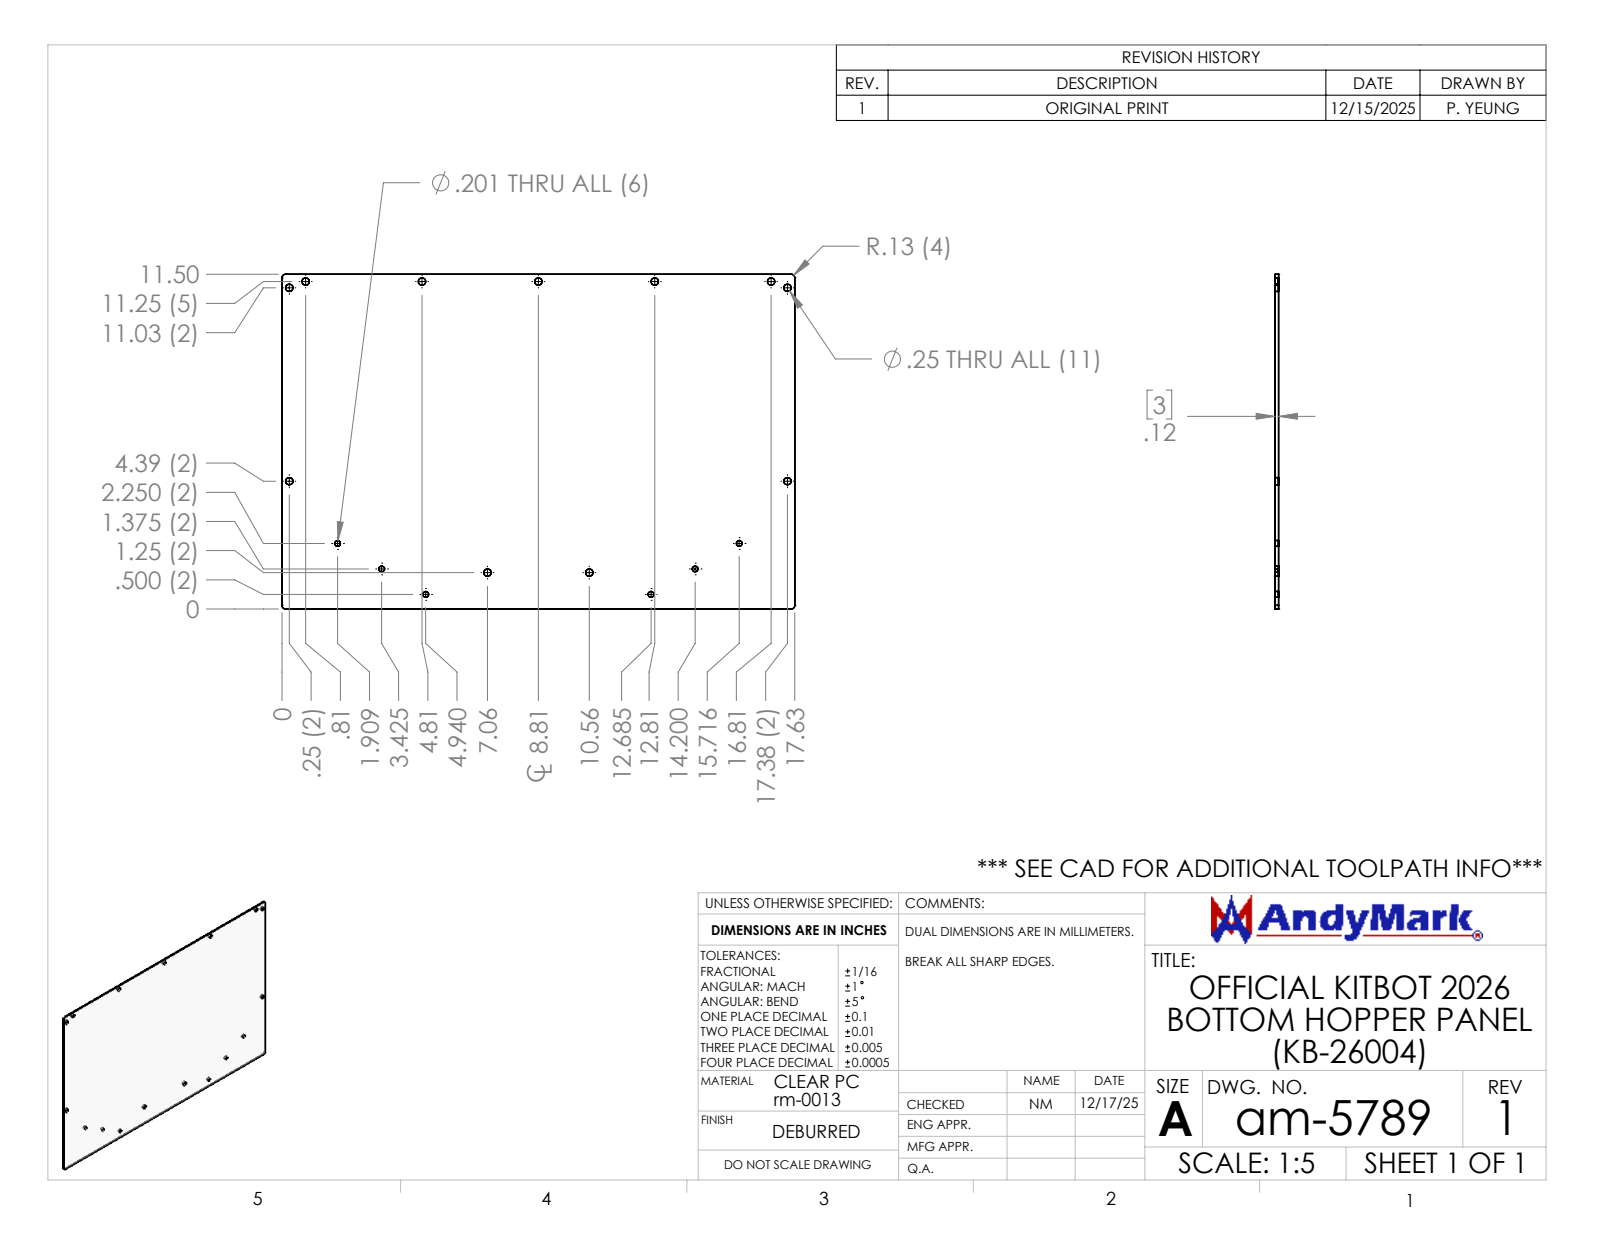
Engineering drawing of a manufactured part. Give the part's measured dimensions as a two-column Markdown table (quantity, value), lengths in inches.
| quantity | value |
| --- | --- |
| part name | am-5789 Bottom Hopper Panel (KB-26004) |
| STEP written by | SolidWorks 2024 (AUTOMOTIVE_DESIGN) |
| units | inches |
| bodies | 1 solid, 44 faces (6 planar, 38 cylindrical, 0 other) |
| overall size | 17.625 × 11.5 × 0.118 |
| volume | 23.85 in³ |
| surface area | 412.2 in² |
| round holes (diameter × count) | 0.25 × 11, 0.201 × 6 |
| partial cylindrical surfaces (radius × count) | 0.125 × 4 |
| main face-to-face distances | 0.118, 11.5, 17.625 |
| hole center spacings | 4, 1.75, 8, 2.251, 2.709, 3.5, 4.379, 5.672 |
